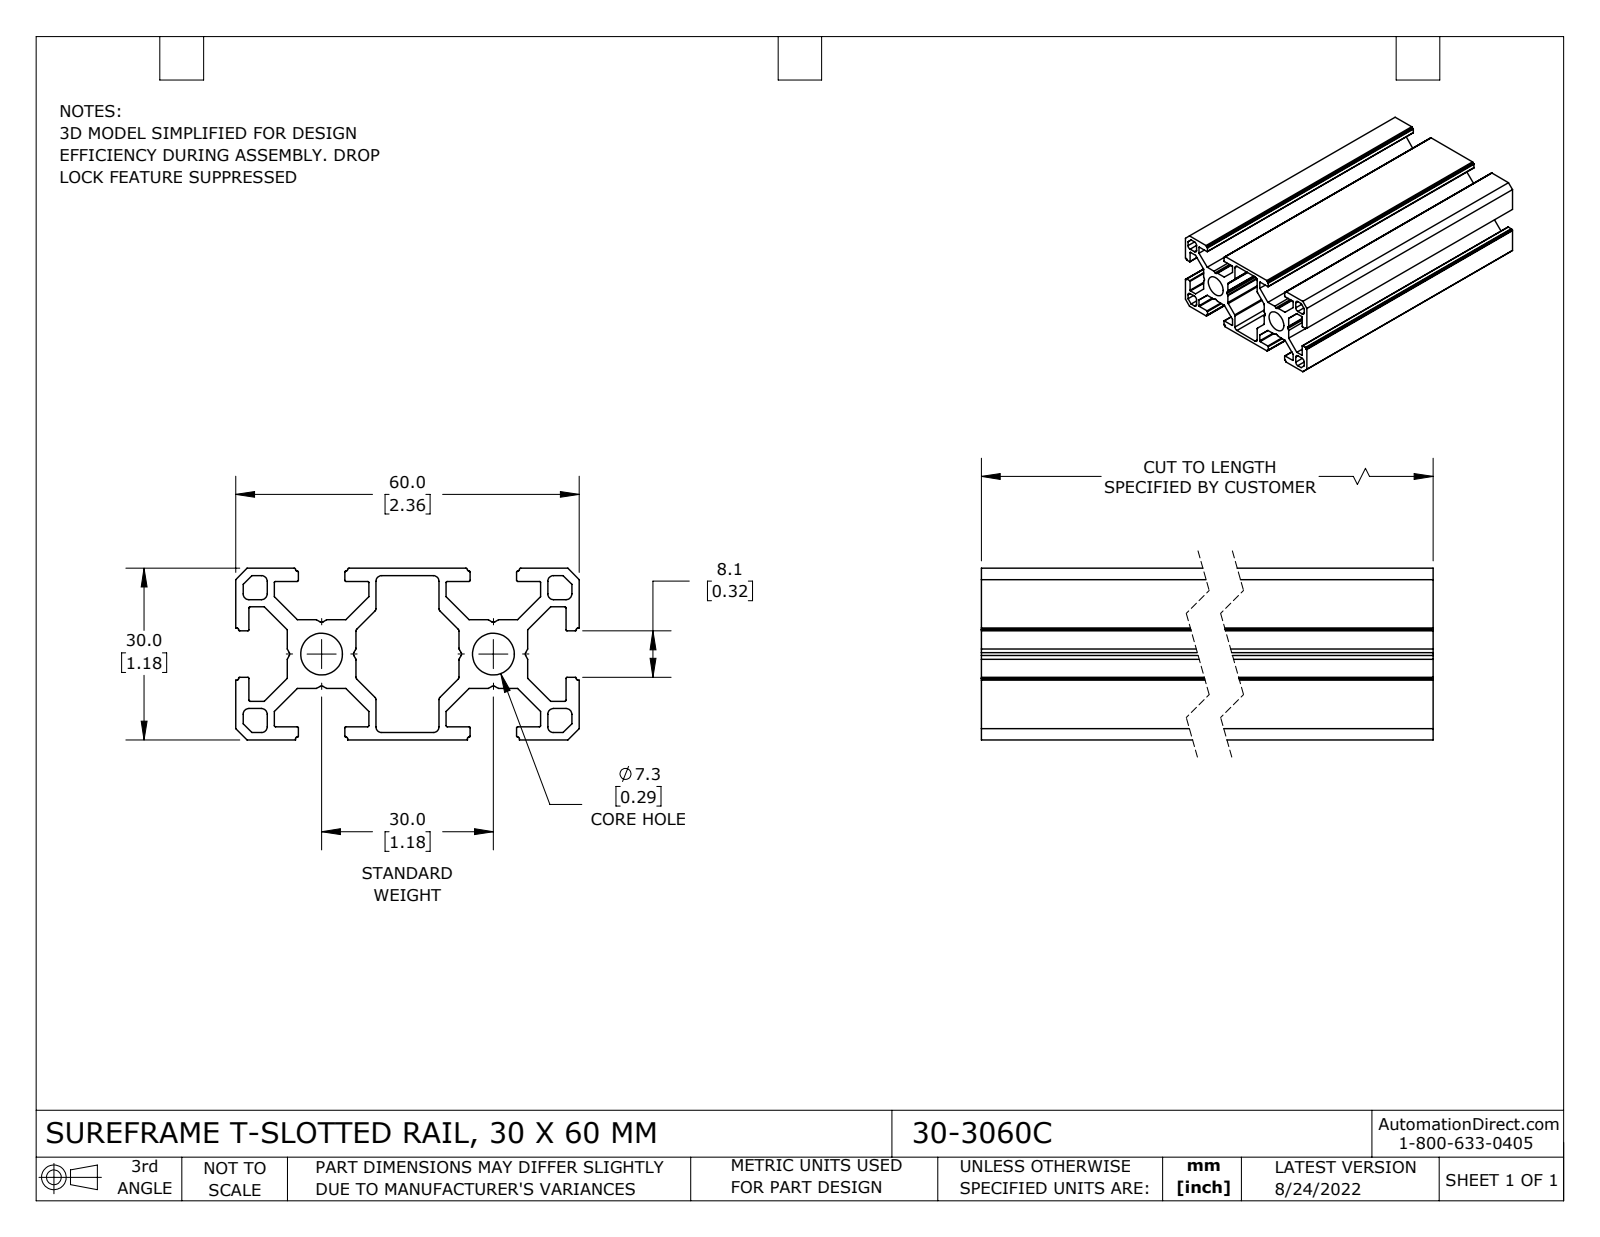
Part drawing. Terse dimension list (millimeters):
name: 30-3060C
written by: SolidWorks 2021 (CONFIG_CONTROL_DESIGN)
unit: mm
bodies: 1 solid, 240 faces (146 planar, 94 cylindrical, 0 other)
size: 101.6 × 60 × 30
volume: 58 625 mm³; area: 55 802 mm²
holes: 2× ⌀7.3
rounds: 36× R0.2, 20× R0.5, 16× R0.25, 16× R1
face distances: 30, 2.32, 9, 6.68, 21, 18.68, 17.75, 2.49, 21.21, 1.3
hole spacings: 30
